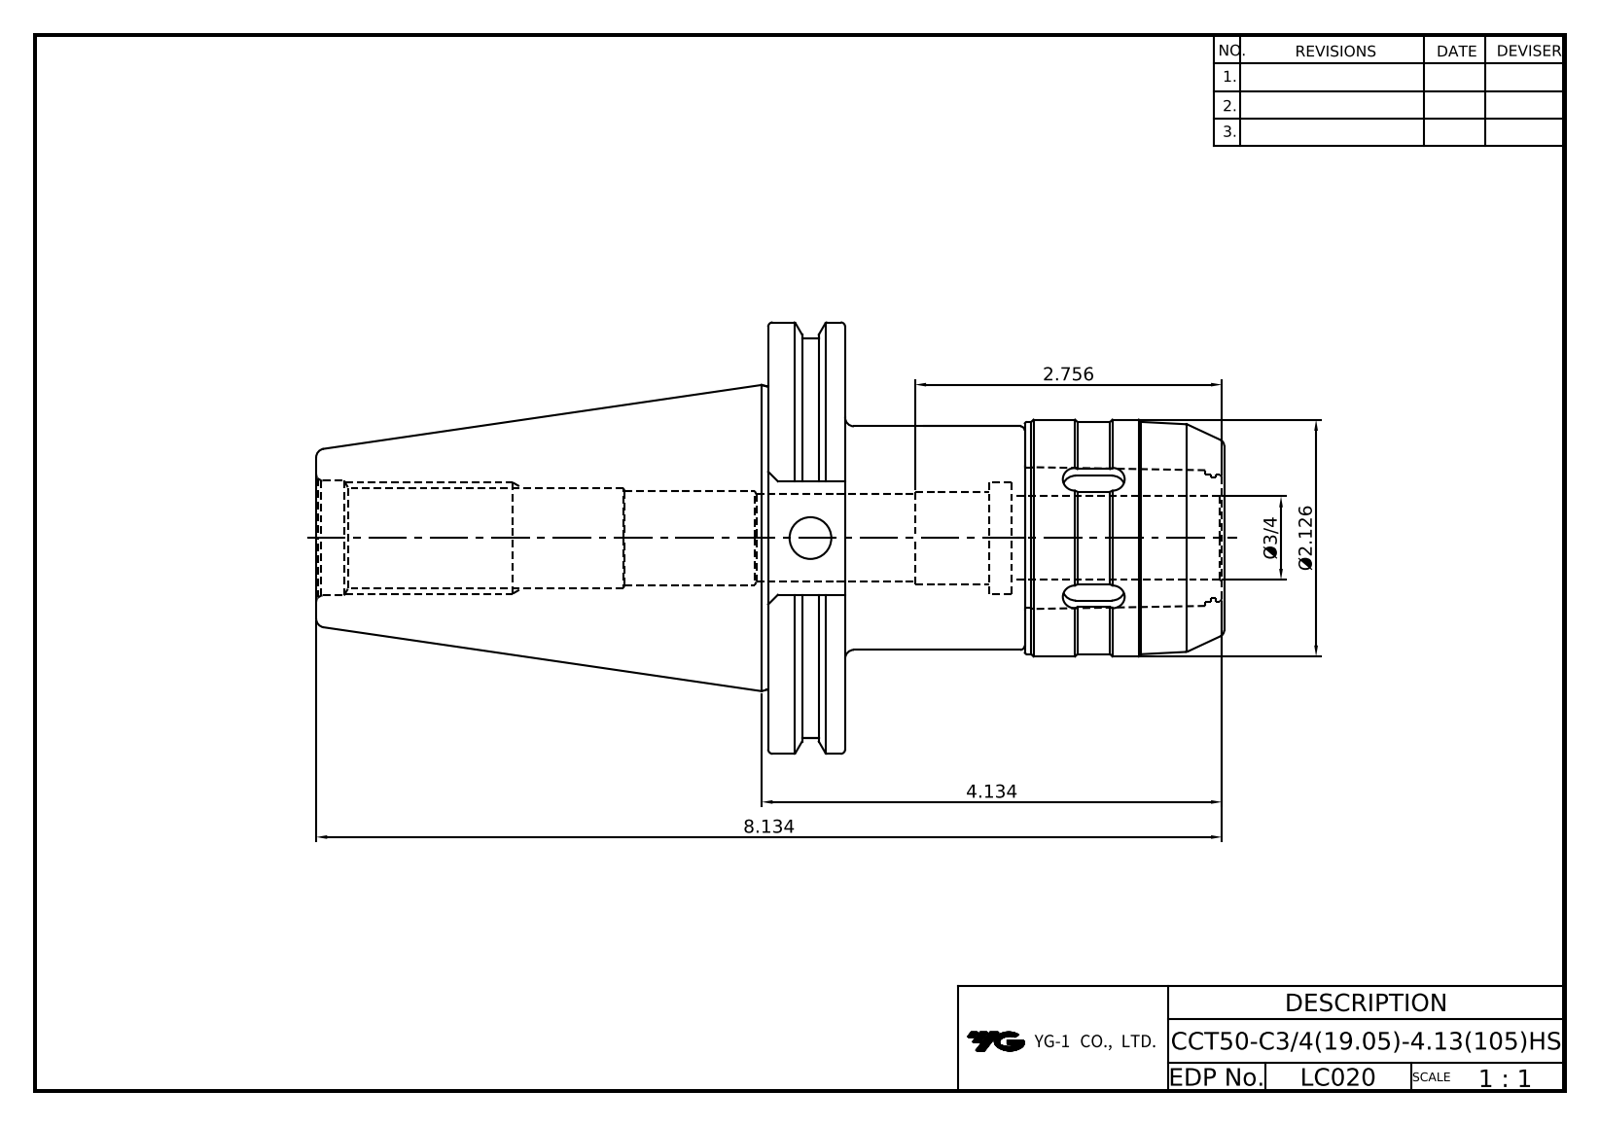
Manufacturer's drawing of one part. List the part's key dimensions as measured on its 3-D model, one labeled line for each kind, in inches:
Part name (STEP PRODUCT): LC020-CCT50-C0_75-4_13HS; C20_CAP; LC020-CCT50-C0_75-4_13HS_ASM
STEP written by: PRO/ENGINEER BY PARAMETRIC TECHNOLOGY CORPORATION, 2012130 (CONFIG_CONTROL_DESIGN)
Units: inches
Bodies: 2 solids, 220 faces (52 planar, 68 cylindrical, 100 other)
Overall size (bounding box): 8.153 × 3.874 × 3.737
Volume: 28.63 in³ · Surface area: 118.6 in²
Round holes (diameter × count): ⌀0.375 ×1, ⌀0.75 ×1, ⌀0.787 ×1, ⌀0.827 ×1, ⌀0.846 ×1, ⌀0.898 ×1, ⌀1.008 ×1, ⌀1.031 ×1, ⌀1.539 ×1, ⌀1.614 ×1
Round bosses / shafts (diameter × count): ⌀3.874 ×1, ⌀3.594 ×1, ⌀2.726 ×1, ⌀2.126 ×1, ⌀2.087 ×1, ⌀2.008 ×1, ⌀1.3 ×1, ⌀1.137 ×1
Partial cylindrical surfaces — rounded edges, fillets, slot ends (radius × count): R0.118 ×10
Main face-to-face distances: 0.691, 2.303, 1.612, 4.059, 4.75, 6.362, 2.882, 0.122, 8.153, 4.094
